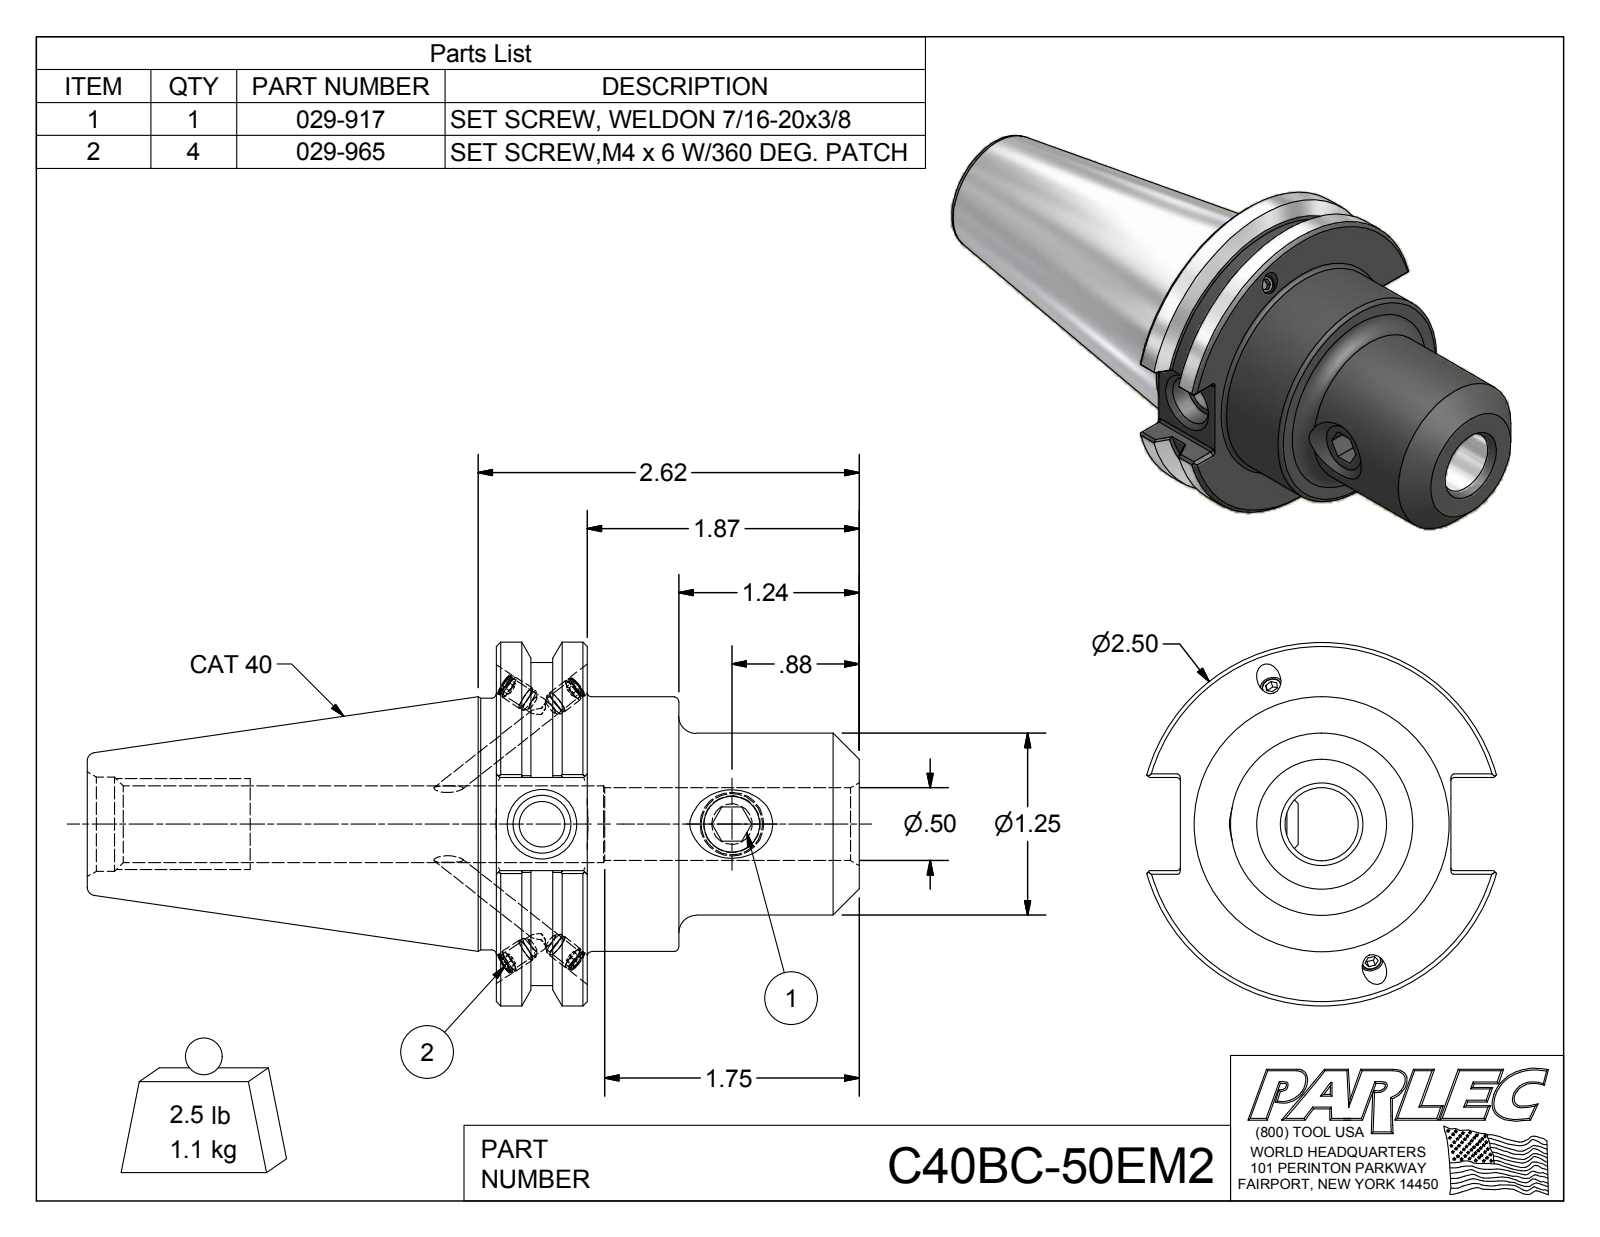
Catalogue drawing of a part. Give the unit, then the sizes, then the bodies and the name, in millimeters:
Units: millimetres
Overall size (bounding box): 134.8 × 63.5 × 61.1
Round holes (diameter × count): ⌀3.3 ×4, ⌀4.1 ×4, ⌀8 ×1, ⌀9.7 ×1, ⌀10.1 ×1, ⌀12.7 ×1, ⌀13.4 ×1, ⌀16.5 ×1
Round bosses / shafts (diameter × count): ⌀4.2 ×4, ⌀4 ×4, ⌀63.5 ×1, ⌀56.4 ×1, ⌀44.5 ×1, ⌀43.9 ×1, ⌀31.8 ×1, ⌀11.1 ×1
Partial cylindrical surfaces — rounded edges, fillets, slot ends (radius × count): R0.5 ×12
Main face-to-face distances: 15.9, 31.9, 16, 63.4, 47.5, 31.5, 6, 16.3, 47.2, 71.4
Hole centre spacings: 33.1
Volume: 142 700 mm³ · Surface area: 28 920 mm²
Bodies: 6 solids, 182 faces (85 planar, 48 cylindrical, 49 other)
Part name (STEP PRODUCT): C40BC-50EM2; C40BC-50EM2-1; 029-917; 029-965
STEP written by: Autodesk Inventor 2012 (AUTOMOTIVE_DESIGN)
